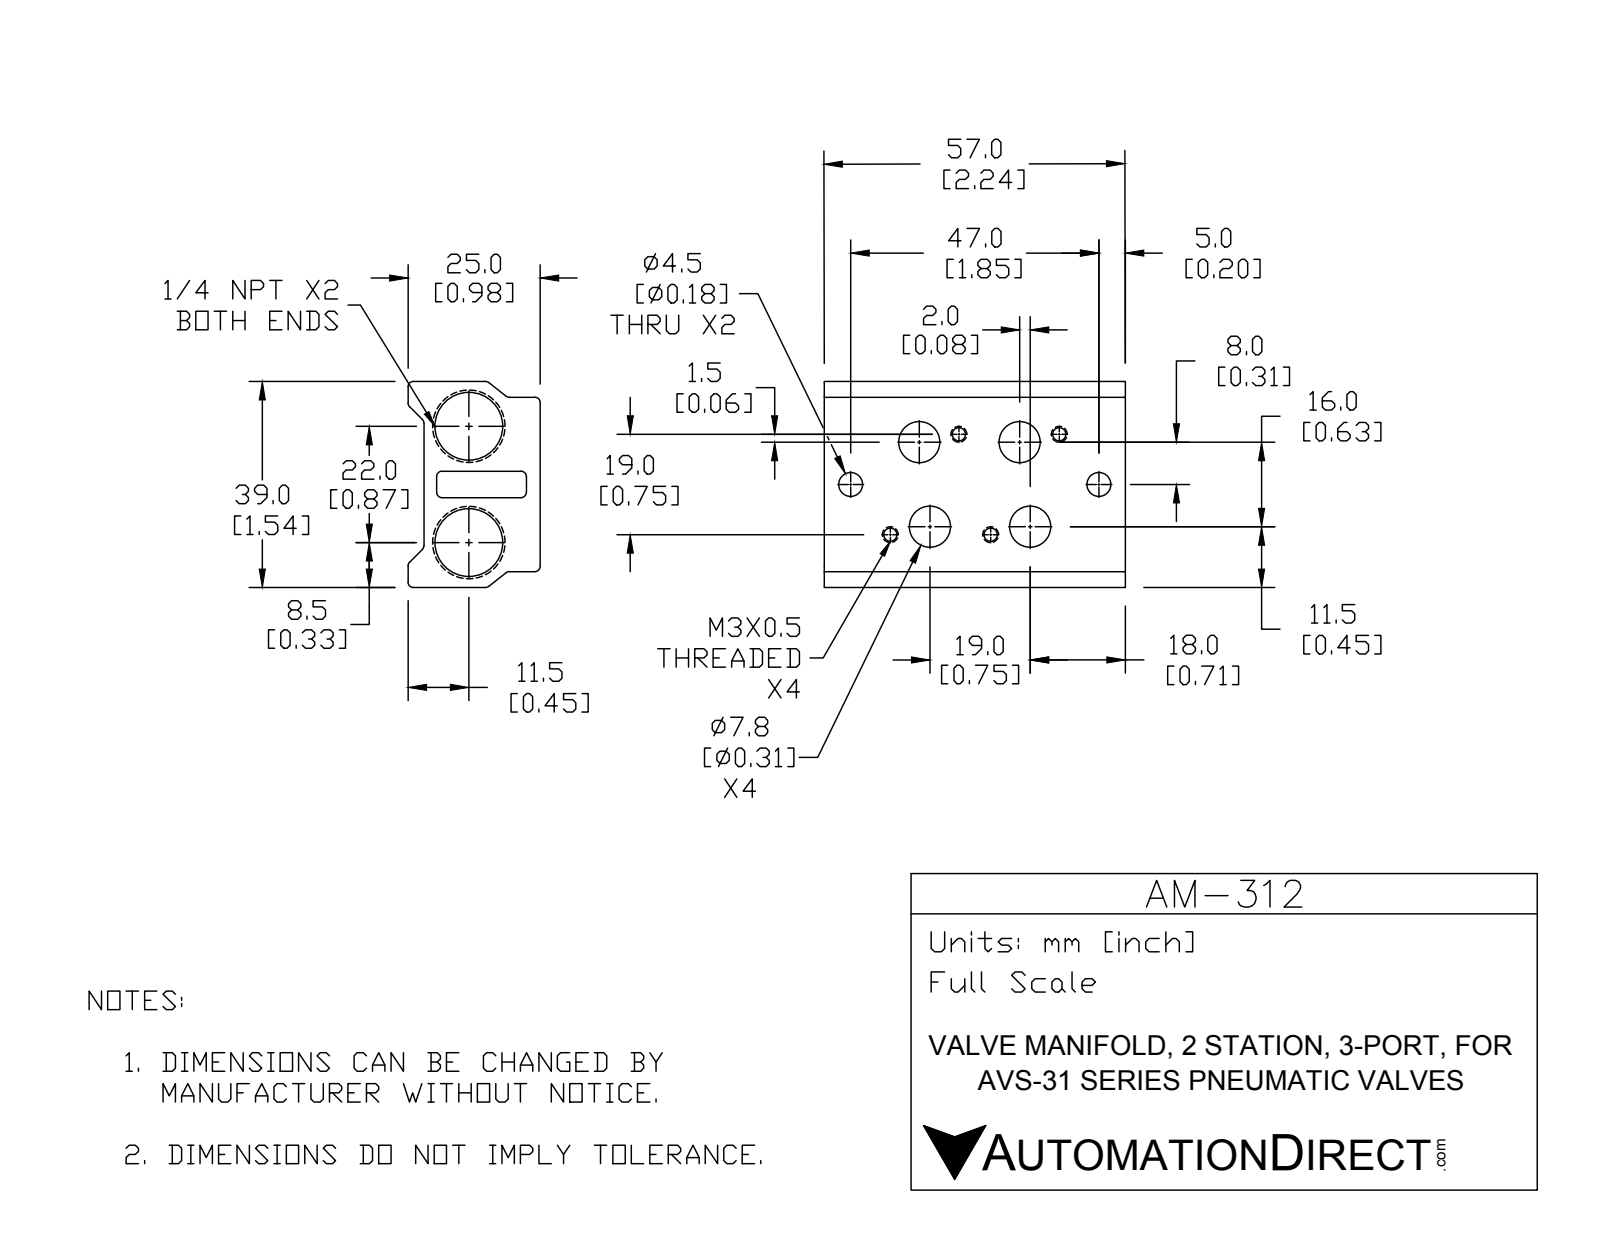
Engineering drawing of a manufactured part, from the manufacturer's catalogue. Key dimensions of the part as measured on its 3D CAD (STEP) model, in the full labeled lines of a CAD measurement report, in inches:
Part name (STEP PRODUCT): AM-312
STEP written by: SolidWorks 2016 (AUTOMOTIVE_DESIGN)
Units: inches
Bodies: 1 solid, 126 faces (26 planar, 62 cylindrical, 38 other)
Overall size (bounding box): 2.244 × 1.535 × 0.984
Volume: 1.738 in³ · Surface area: 24.22 in²
Round holes (diameter × count): ⌀0.098 ×4, ⌀0.307 ×4, ⌀0.177 ×2, ⌀0.437 ×2, ⌀0.438 ×2
Partial cylindrical surfaces — rounded edges, fillets, slot ends (radius × count): R0.039 ×16
Main face-to-face distances: 0.866, 0.669, 0.118, 0.197, 1.535, 1.417, 0.551, 0.748, 2.244, 0.984
Hole centre spacings: 0.301, 0.722, 0.748, 0.457, 0.476, 0.601, 0.635, 0.669
